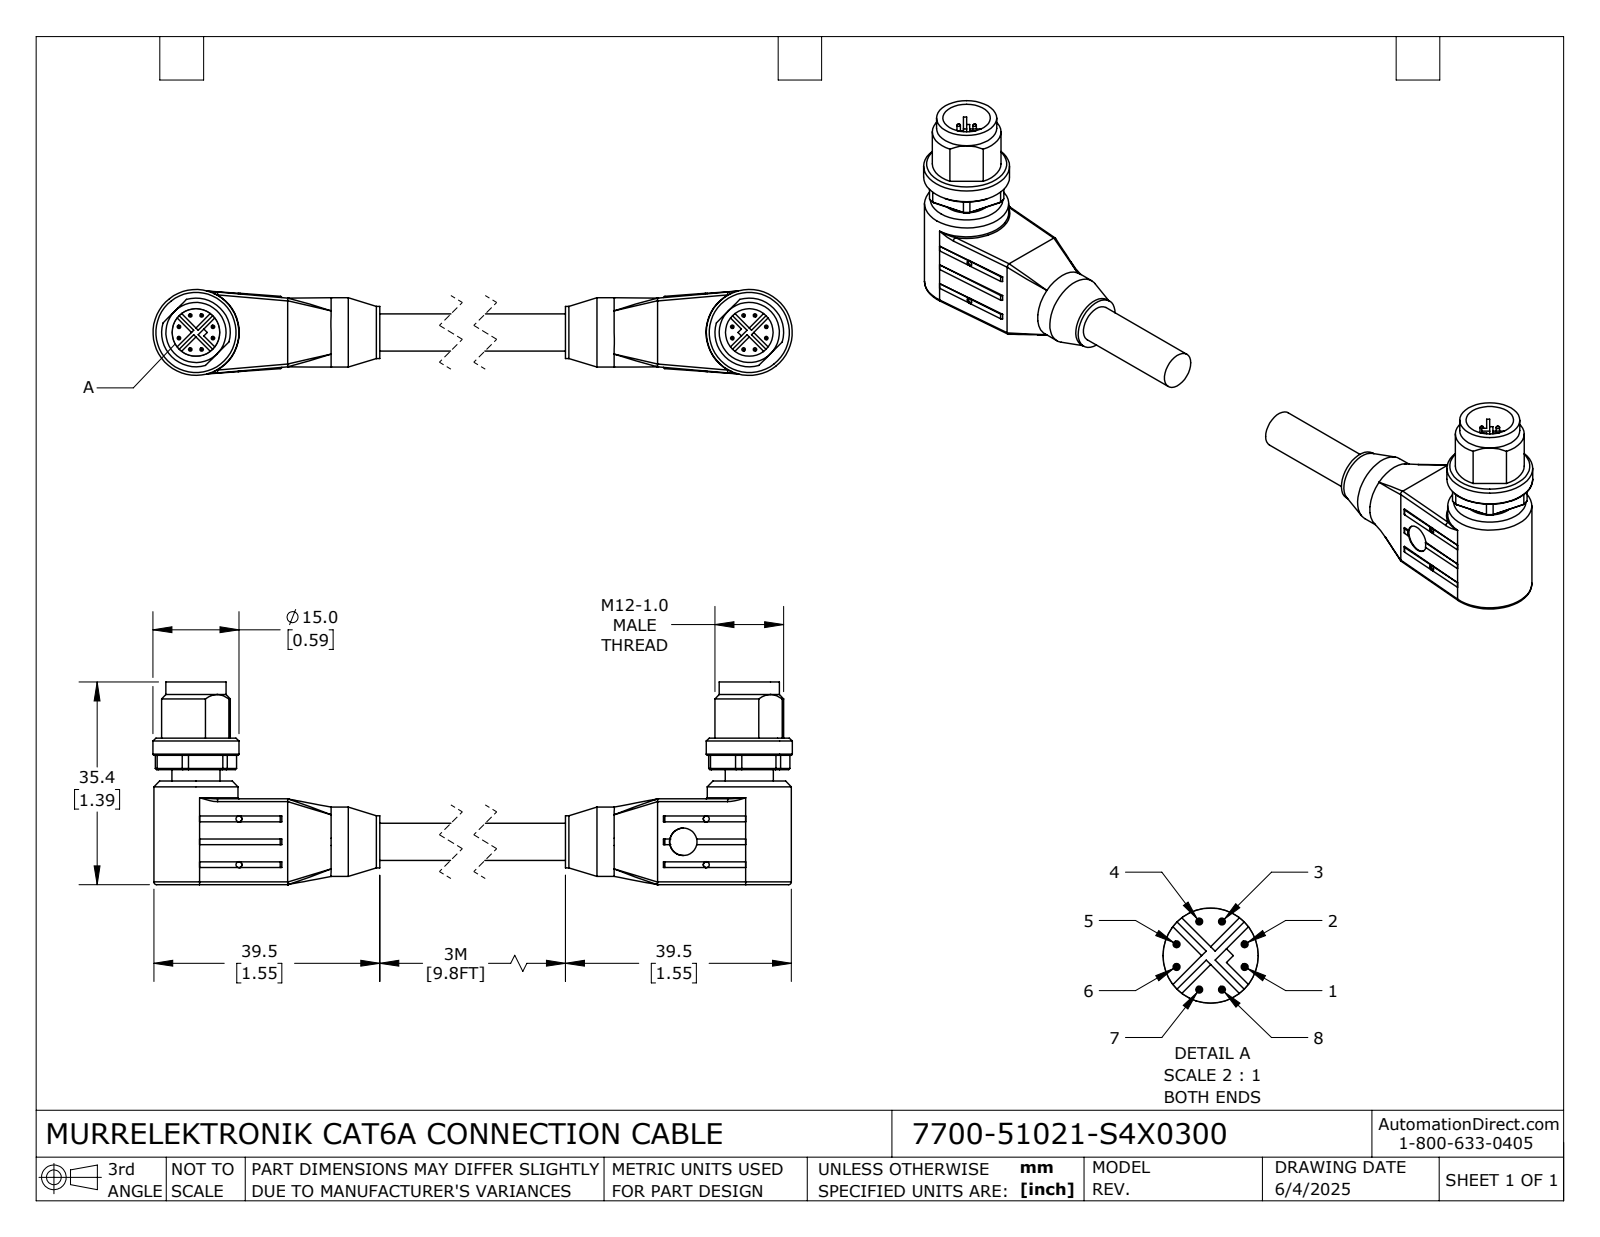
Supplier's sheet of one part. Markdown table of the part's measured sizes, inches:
| quantity | value |
| --- | --- |
| part name | 7700-51021-S4X0300; 7700-51021-S4X0300_MALE |
| STEP written by | SolidWorks 2024 (CONFIG_CONTROL_DESIGN) |
| units | inches |
| bodies | 2 solids, 424 faces (196 planar, 134 cylindrical, 94 other) |
| overall size | 5.677 × 1.394 × 0.591 |
| volume | 1.124 in³ |
| surface area | 12.42 in² |
| round holes (diameter × count) | 0.041 × 8, 0.189 × 2, 0.327 × 2 |
| round bosses / shafts (diameter × count) | 0.024 × 16, 0.591 × 2, 0.579 × 2, 0.413 × 2, 0.331 × 2, 0.476 × 1, 0.358 × 1, 0.256 × 1 |
| partial cylindrical surfaces (radius × count) | 0.02 × 8, 0.012 × 4, 0.236 × 2, 0.283 × 2 |
| main face-to-face distances | 0.141, 0.591, 3.596, 0.791, 0.201, 0.713, 0.122, 0.079, 0.043, 0.185 |
| hole center spacings | 0.315, 4.521, 4.532, 4.208, 5.087 |
